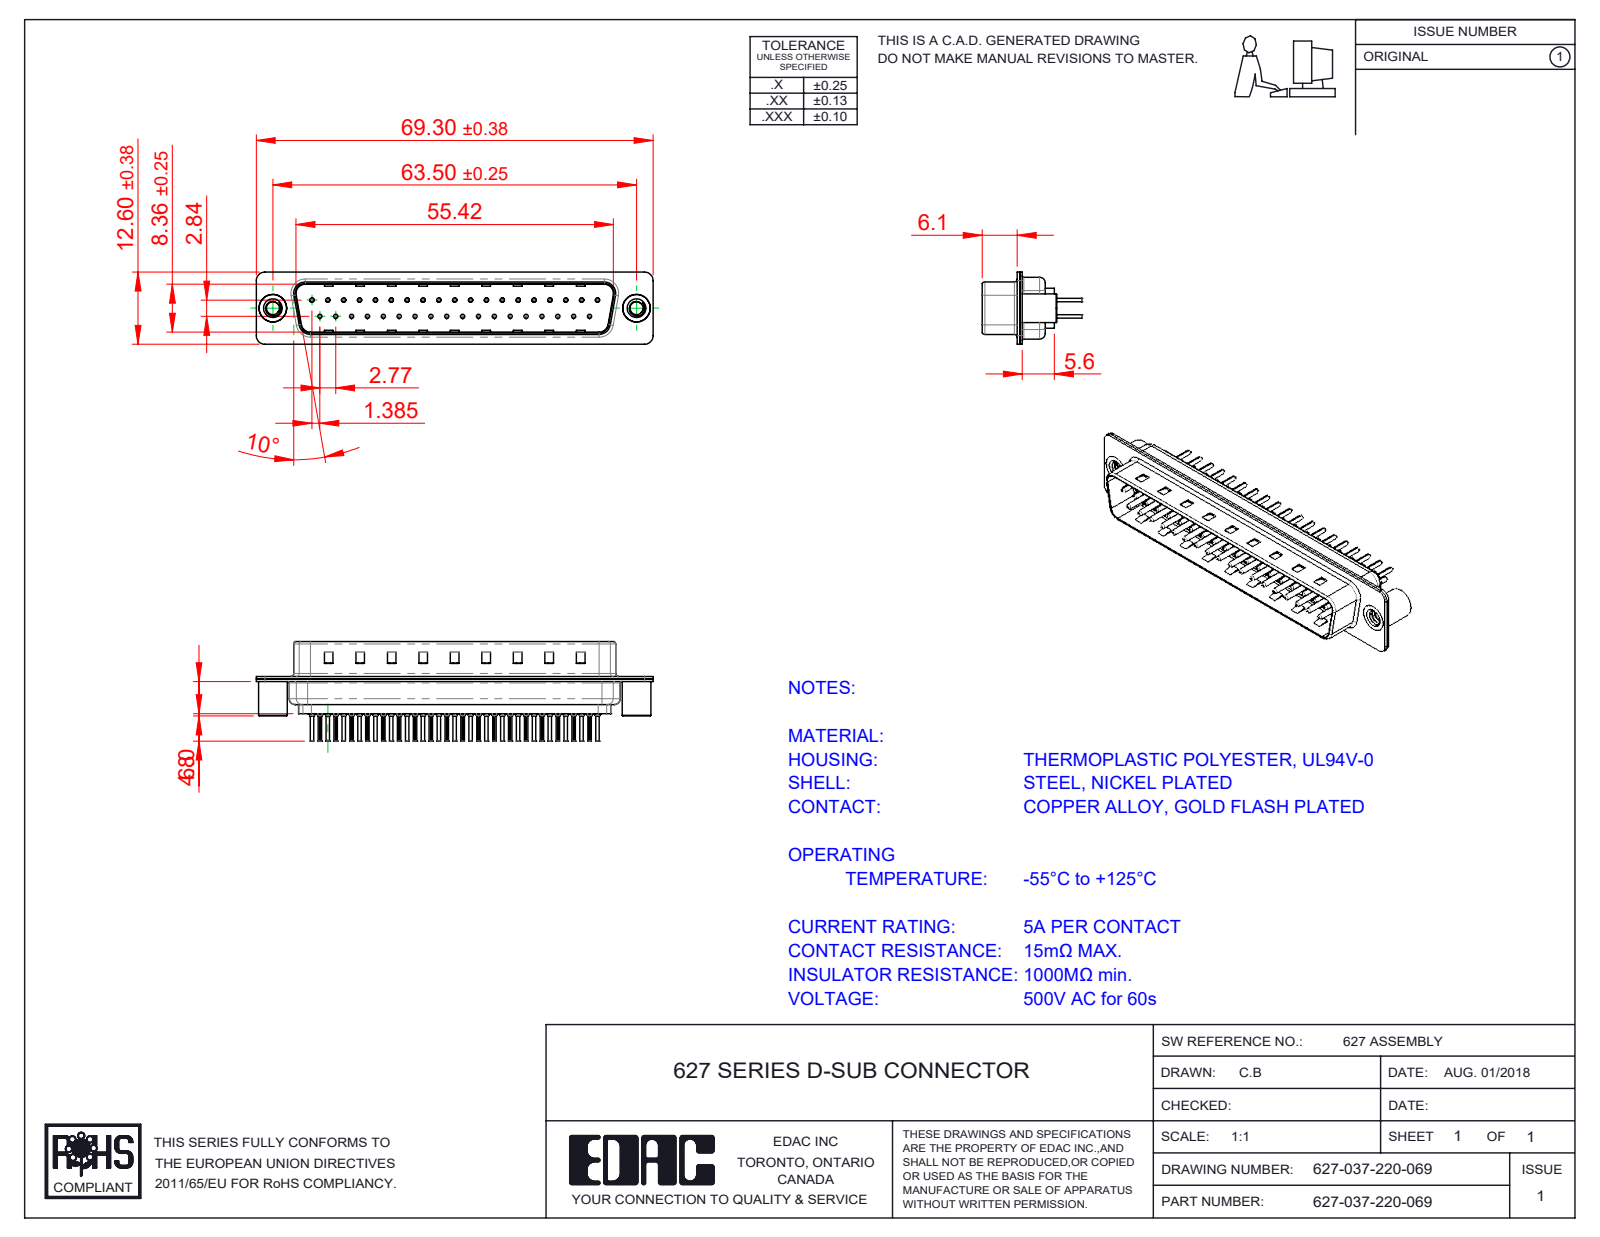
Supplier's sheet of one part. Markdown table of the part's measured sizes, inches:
| quantity | value |
| --- | --- |
| part name | 627 Housing_37 LP; 627 Contact Row 2_20L; 627 Contact Row 1_20L; 627-037-220-069 (+3 more) |
| STEP written by | SolidWorks 2020 (CONFIG_CONTROL_DESIGN) |
| units | inches |
| bodies | 42 solids, 4060 faces (1091 planar, 1530 cylindrical, 1439 other) |
| overall size | 2.728 × 0.681 × 0.496 |
| volume | 0.232 in³ |
| surface area | 16.85 in² |
| round holes (diameter × count) | 0.008 × 37, 0.014 × 37, 0.043 × 37, 0.063 × 37, 0.089 × 2, 0.157 × 2, 0.189 × 2 |
| round bosses / shafts (diameter × count) | 0.079 × 37, 0.059 × 37, 0.03 × 37, 0.024 × 37, 0.197 × 2, 0.193 × 2 |
| partial cylindrical surfaces (radius × count) | 0.004 × 74, 0.059 × 16, 0.079 × 12, 0.02 × 8, 0.063 × 8, 0.01 × 4, 0.024 × 4, 0.026 × 4 |
| main face-to-face distances | 0.016, 0.032, 0.377, 0.018, 0.345, 0.059, 0.035, 0.055, 0.256, 0.238 |
| hole center spacings | 0.124, 0.109, 0.218, 0.327, 0.198, 0.398, 0.436, 0.503 |
